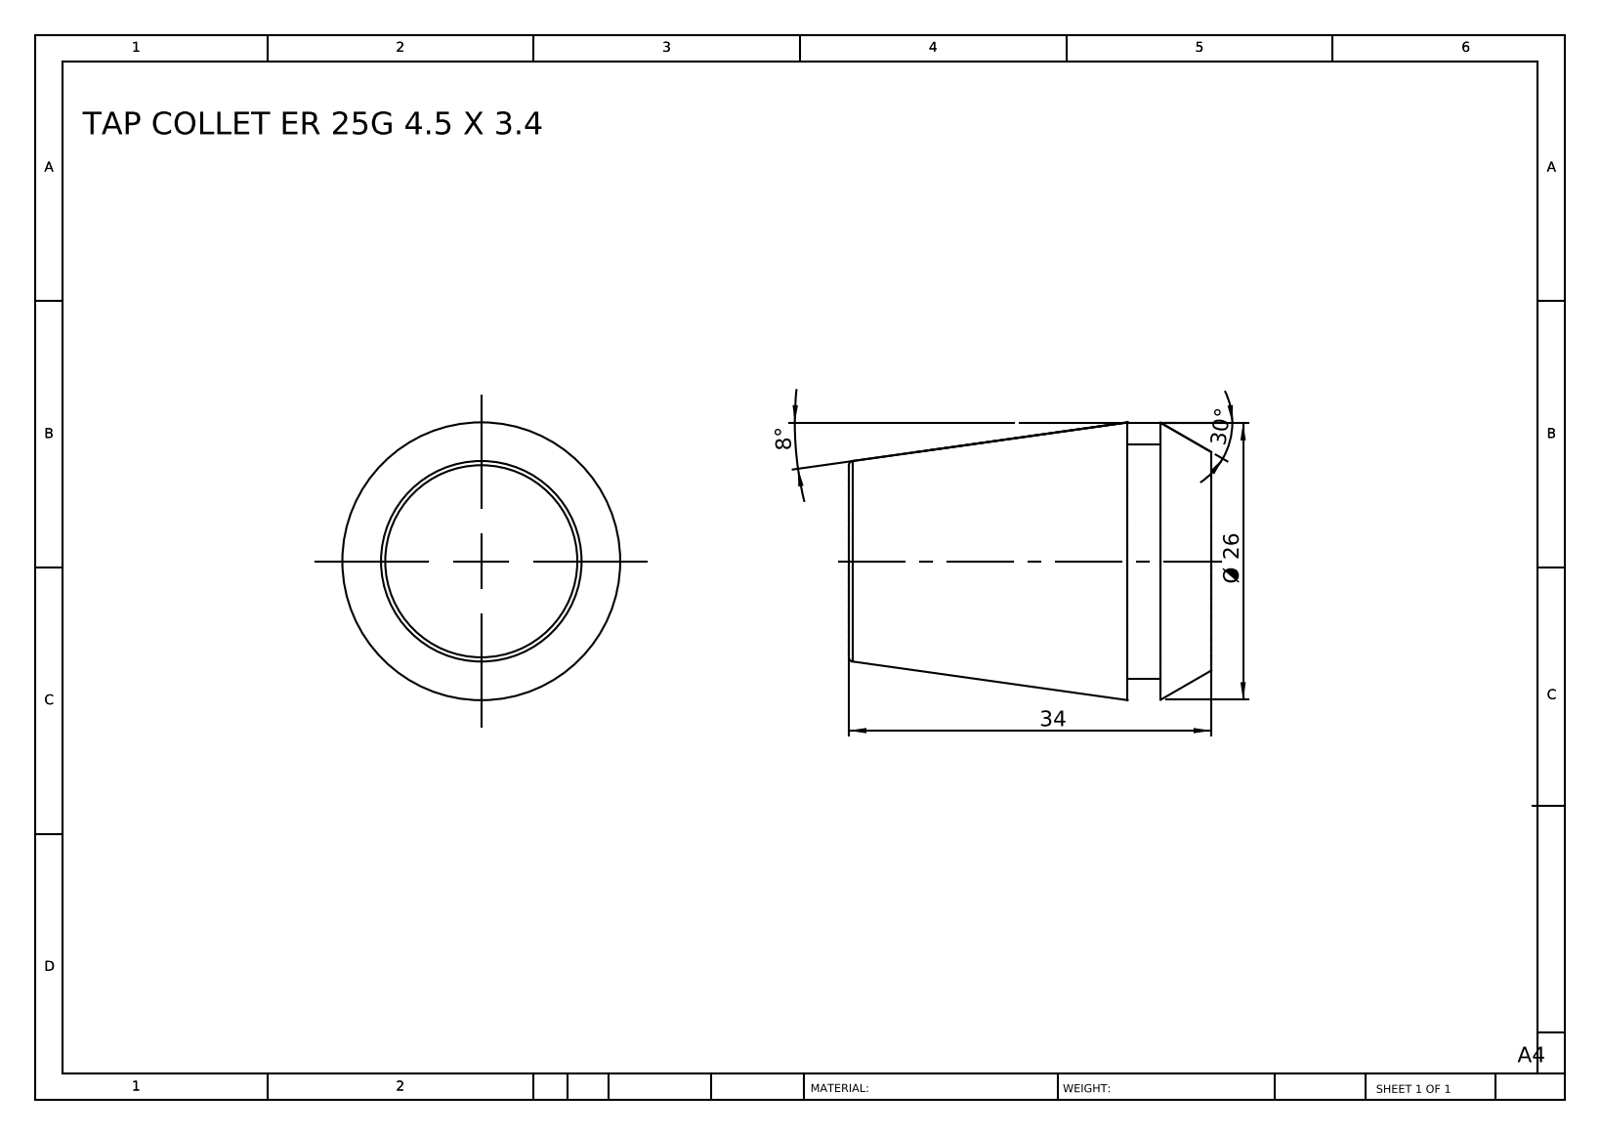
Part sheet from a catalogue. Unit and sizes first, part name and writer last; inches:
Units: inches
Overall size (bounding box): 1.339 × 1.026 × 1.026
Round bosses / shafts (diameter × count): ⌀0.866 ×1
Main face-to-face distances: 1.339, 0.309, 1.03, 0.187, 0.122, 1.152
Volume: 0.83 in³ · Surface area: 5.233 in²
Bodies: 1 solid, 12 faces (4 planar, 2 cylindrical, 6 other)
Part name (STEP PRODUCT): TAP COLLET ER 25G 4.5 X 3.4
STEP written by: SolidWorks 2014 (CONFIG_CONTROL_DESIGN)
